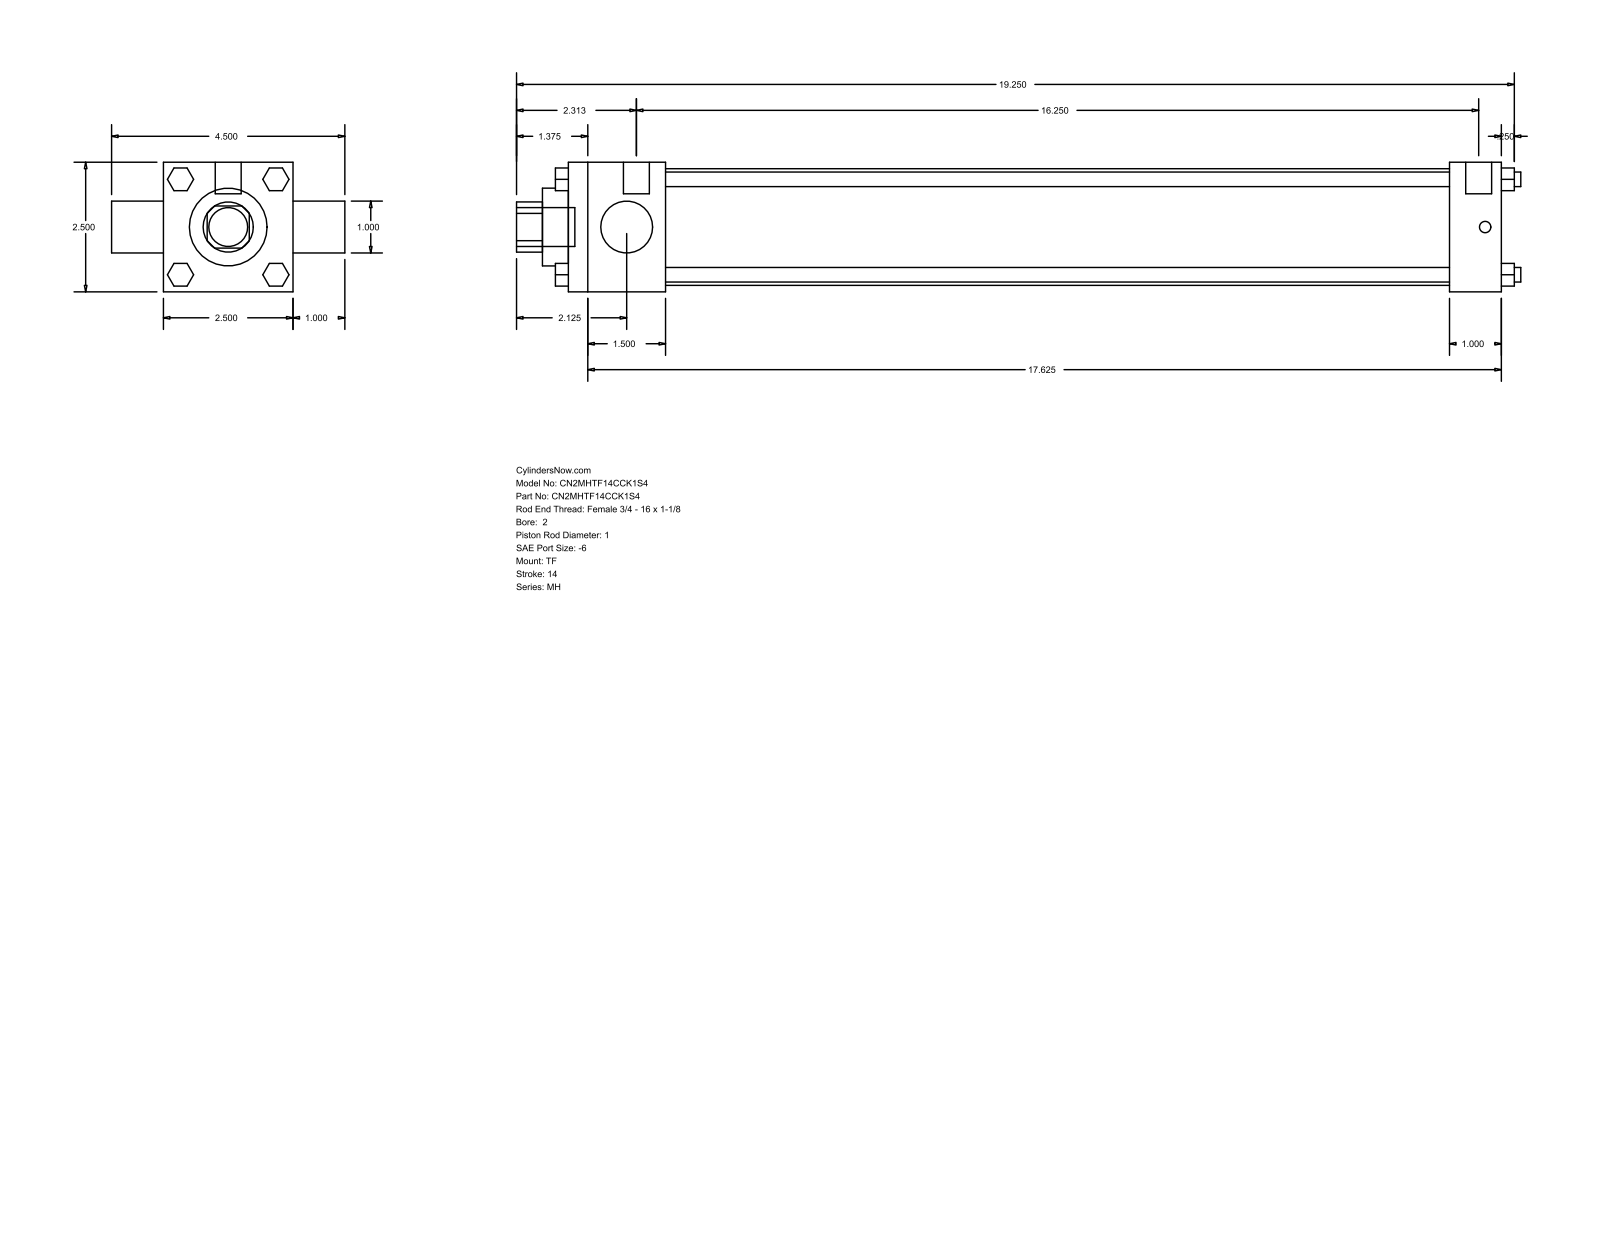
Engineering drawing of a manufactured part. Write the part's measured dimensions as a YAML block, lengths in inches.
part_name: "MH_TF__0200_1"
step_written_by: "GSSL Pune (CONFIG_CONTROL_DESIGN)"
units: inches
bodies: {solids: 0, faces: 120, planar: 92, cylindrical: 28, other: 0}
overall_size: [19.375, 4.5, 2.5]
round_holes:
  - {diameter: 1, count: 2}
  - {diameter: 1.5, count: 1}
  - {diameter: 2.25, count: 1}
round_bosses_or_shafts:
  - {diameter: 0.281, count: 4}
  - {diameter: 0.219, count: 3}
  - {diameter: 0.5, count: 2}
  - {diameter: 0.75, count: 1}
partial_cylinders:
  - {radius: 0.484, count: 1}
face_to_face_distances: [2.5, 18, 1, 1.875, 17, 15.125, 16.125, 3.5, 18.5, 0.25]
